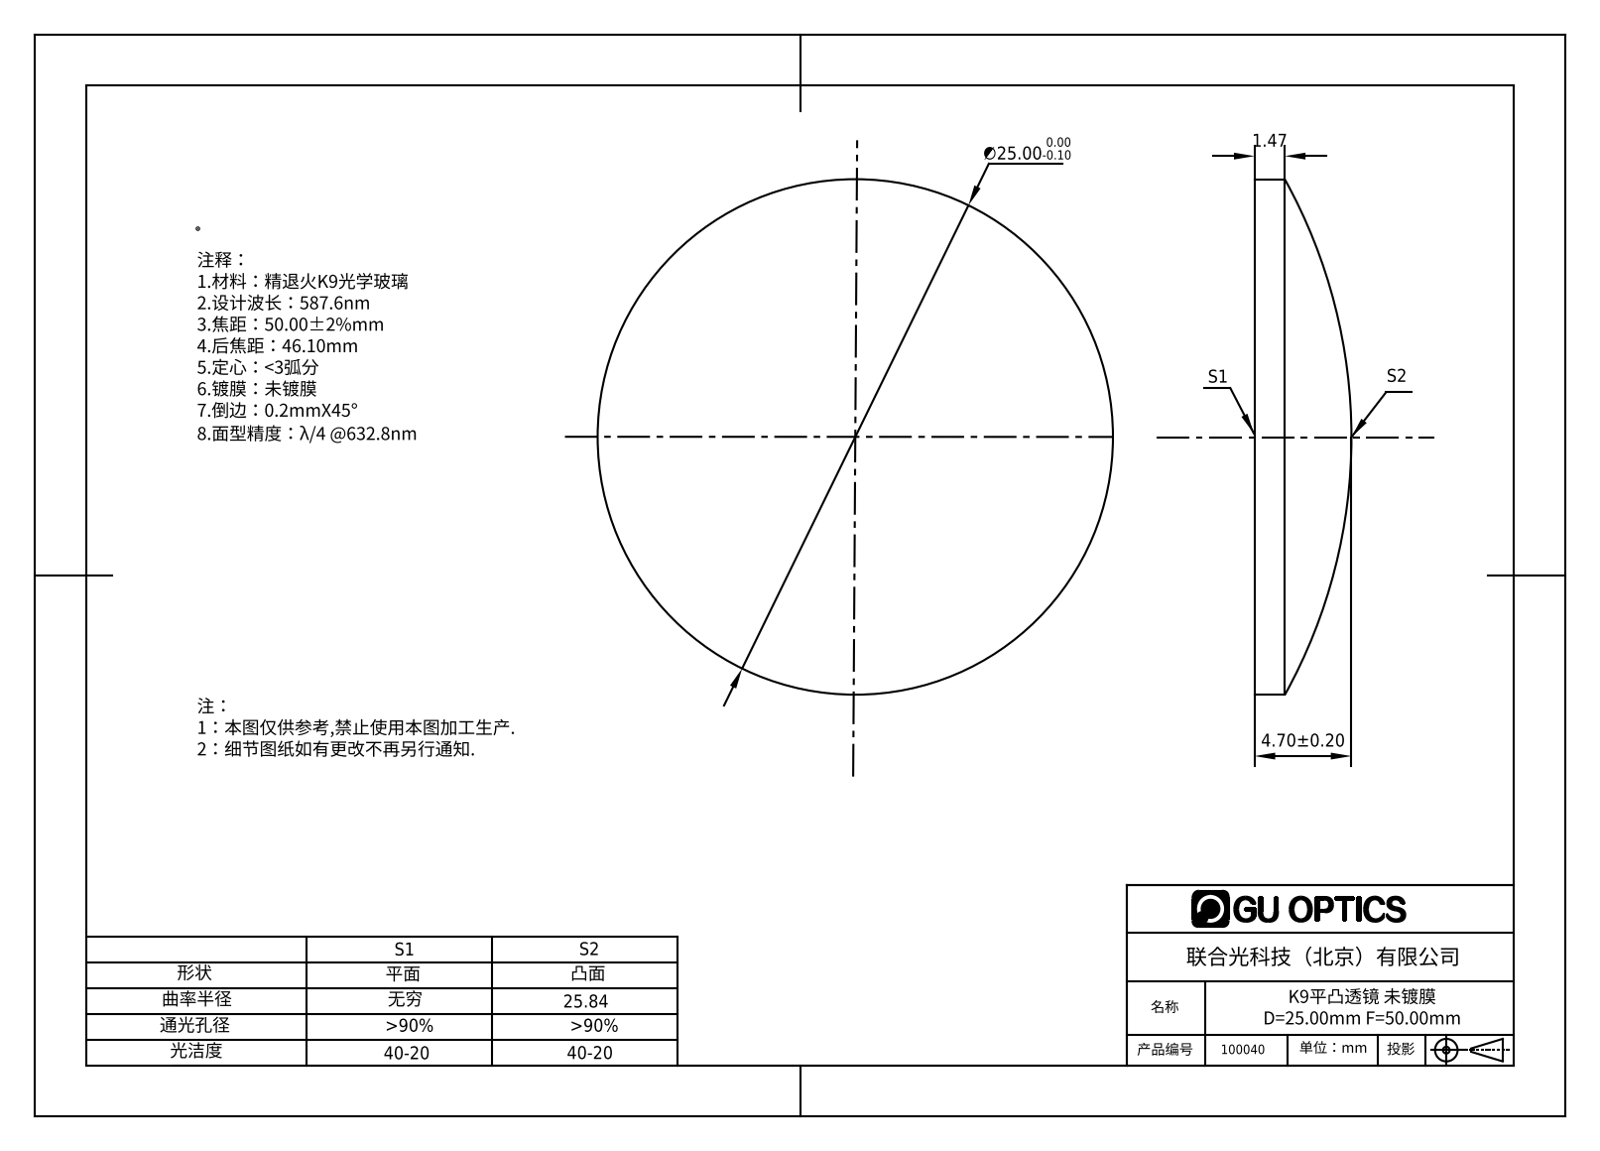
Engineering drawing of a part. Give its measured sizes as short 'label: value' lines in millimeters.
name: 100040
written by: SolidWorks 2016 (AUTOMOTIVE_DESIGN)
unit: mm
bodies: 1 solid, 5 faces (1 planar, 2 cylindrical, 2 other)
size: 25 × 25 × 4.7
volume: 1 532 mm³; area: 1 130 mm²
bosses: 1× ⌀25
